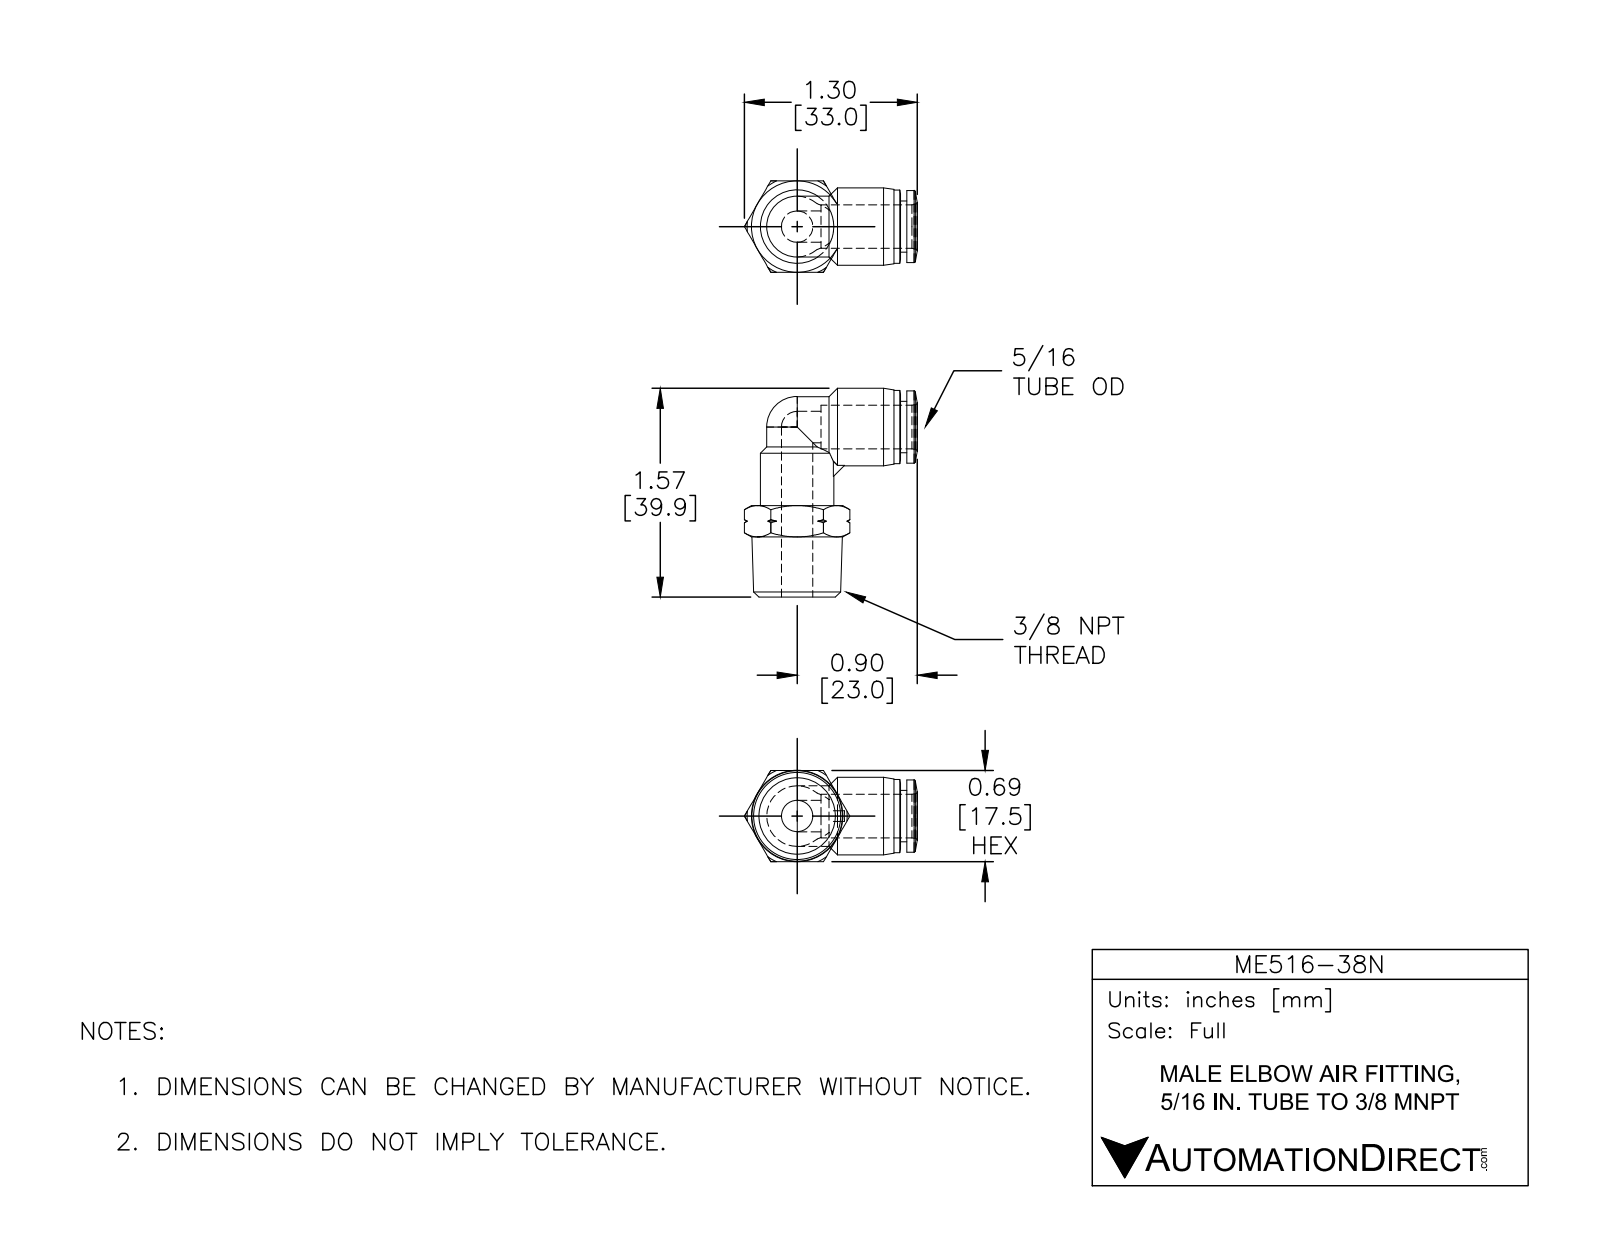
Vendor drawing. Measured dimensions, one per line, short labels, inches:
name: ME516-38N
written by: SolidWorks 2015 (CONFIG_CONTROL_DESIGN)
unit: in
bodies: 1 solid, 89 faces (16 planar, 21 cylindrical, 52 other)
size: 1.571 × 1.3 × 0.687
volume: 0.452 in³; area: 6.606 in²
holes: 2× ⌀0.236, 1× ⌀0.327
bosses: 2× ⌀0.551, 1× ⌀0.583, 1× ⌀0.543, 1× ⌀0.457, 1× ⌀0.386
rounds: 1× R0.228
face distances: 0.687, 0.689, 0.047, 0.598, 0.646, 0.304, 0.383, 0.549, 0.049, 0.096
